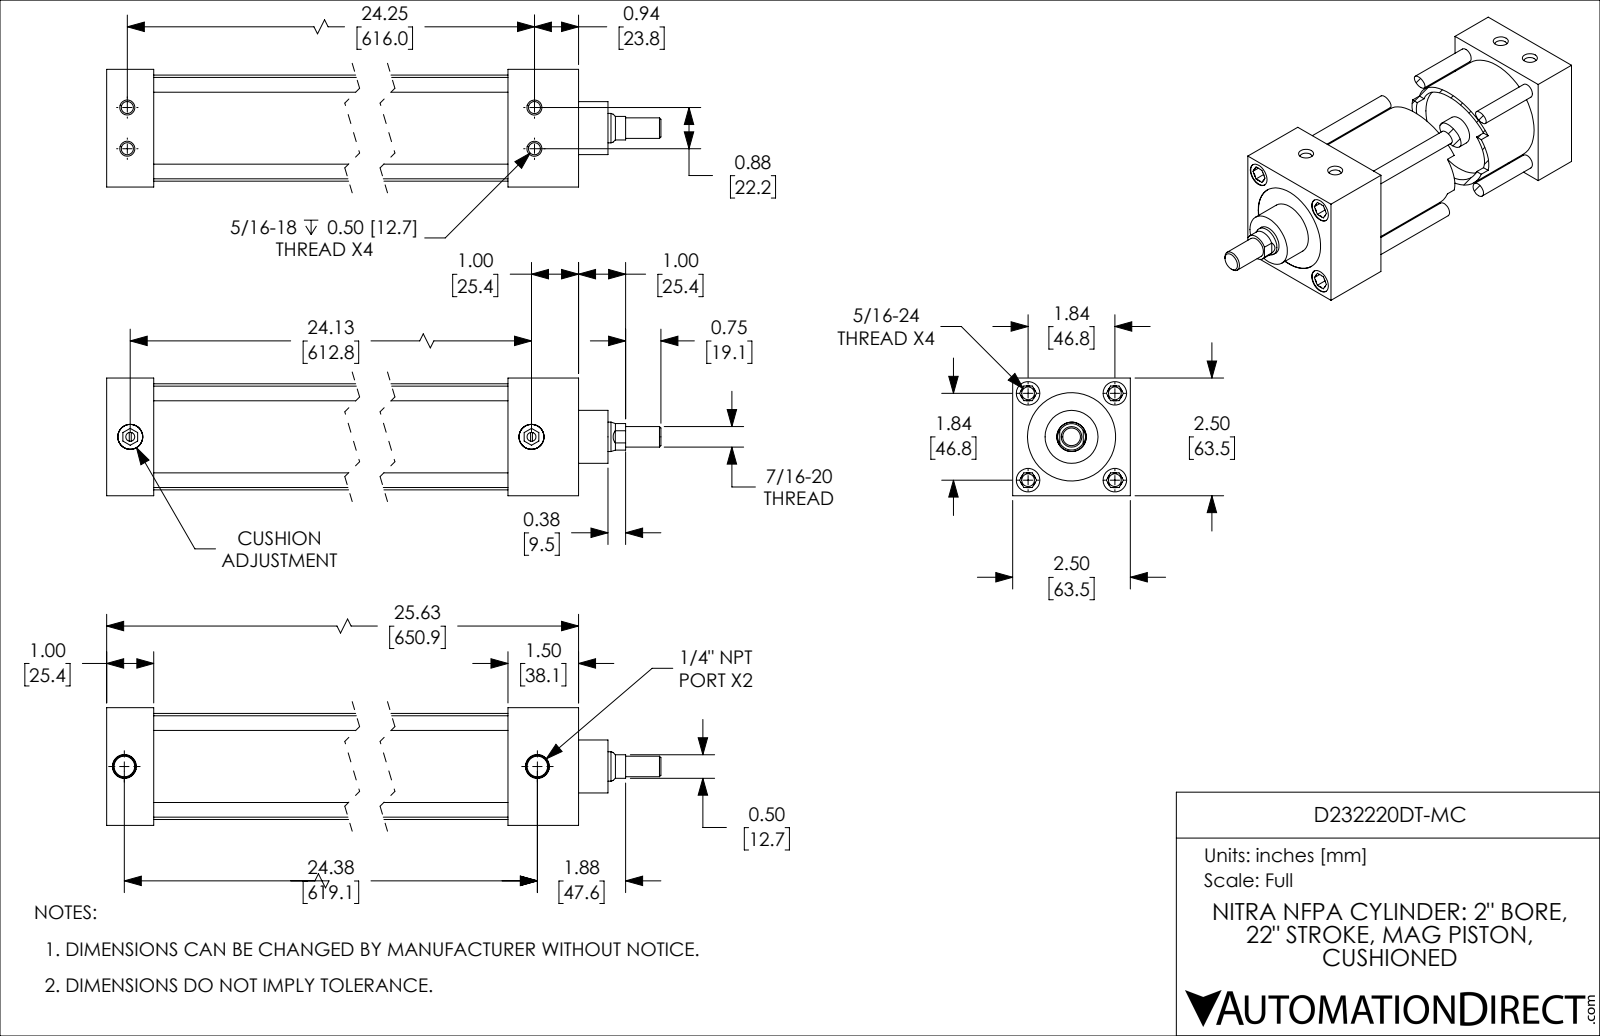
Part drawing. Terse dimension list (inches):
name: D232220DT-MC_PISTON_KK1; D232220DT-MC_CUSHION; D232220DT-MC; D232220DT-MC_BODY
written by: SolidWorks 2019 (CONFIG_CONTROL_DESIGN)
unit: in
bodies: 4 solids, 248 faces (90 planar, 78 cylindrical, 80 other)
size: 27.375 × 2.5 × 2.5
volume: 52.25 in³; area: 527.2 in²
holes: 7× ⌀0.272, 4× ⌀0.257, 4× ⌀0.5, 2× ⌀0.19, 2× ⌀0.438, 2× ⌀0.531, 1× ⌀0.626, 1× ⌀1.875, 1× ⌀2.001
bosses: 4× ⌀0.312, 2× ⌀0.532, 1× ⌀2.251, 1× ⌀1.999, 1× ⌀1.125, 1× ⌀0.624, 1× ⌀0.437
rounds: 1× R0.281
face distances: 2.5, 1, 24.125, 23.125, 1.125, 2.125, 22, 25.625, 24.625, 23.5
hole spacings: 1.84, 1.844, 1.301, 0.441, 0.443, 0.875, 1.304, 2.602
